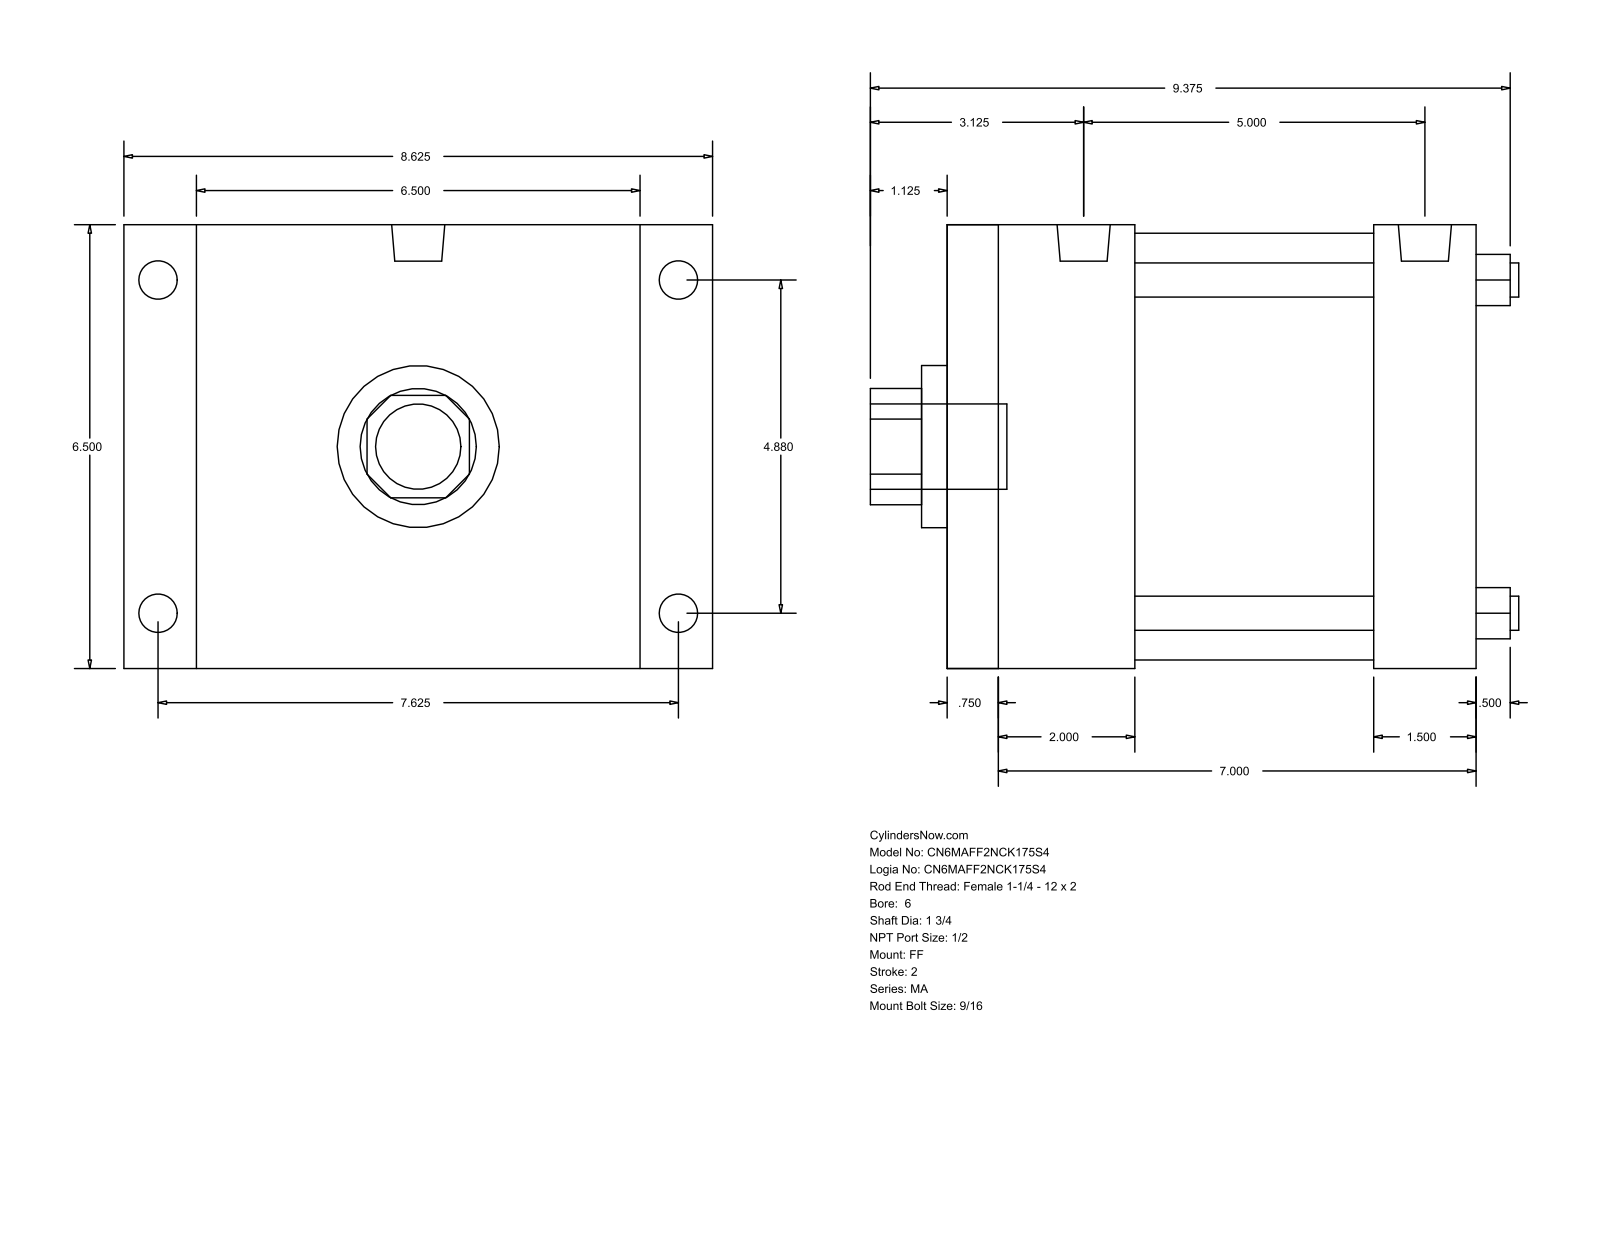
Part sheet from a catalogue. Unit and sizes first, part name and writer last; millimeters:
Units: millimetres
Overall size (bounding box): 241.3 × 219.07 × 165.1
Round holes (diameter × count): ⌀12.7 ×4, ⌀44.45 ×1, ⌀60.33 ×1, ⌀158.75 ×1
Round bosses / shafts (diameter × count): ⌀17.46 ×4, ⌀14.29 ×4, ⌀19.77 ×2, ⌀31.75 ×1
Partial cylindrical surfaces — rounded edges, fillets, slot ends (radius × count): R21.63 ×1
Main face-to-face distances: 165.1, 196.86, 19.05, 177.81, 50.8, 139.7, 69.85, 127.01, 158.75, 88.9
Hole centre spacings: 87.65, 123.96, 175.31
Bodies: 0 solids, 92 faces (64 planar, 28 cylindrical, 0 other)
Part name (STEP PRODUCT): MA_FF__0600_1.75
STEP written by: GSSL Pune (CONFIG_CONTROL_DESIGN)
